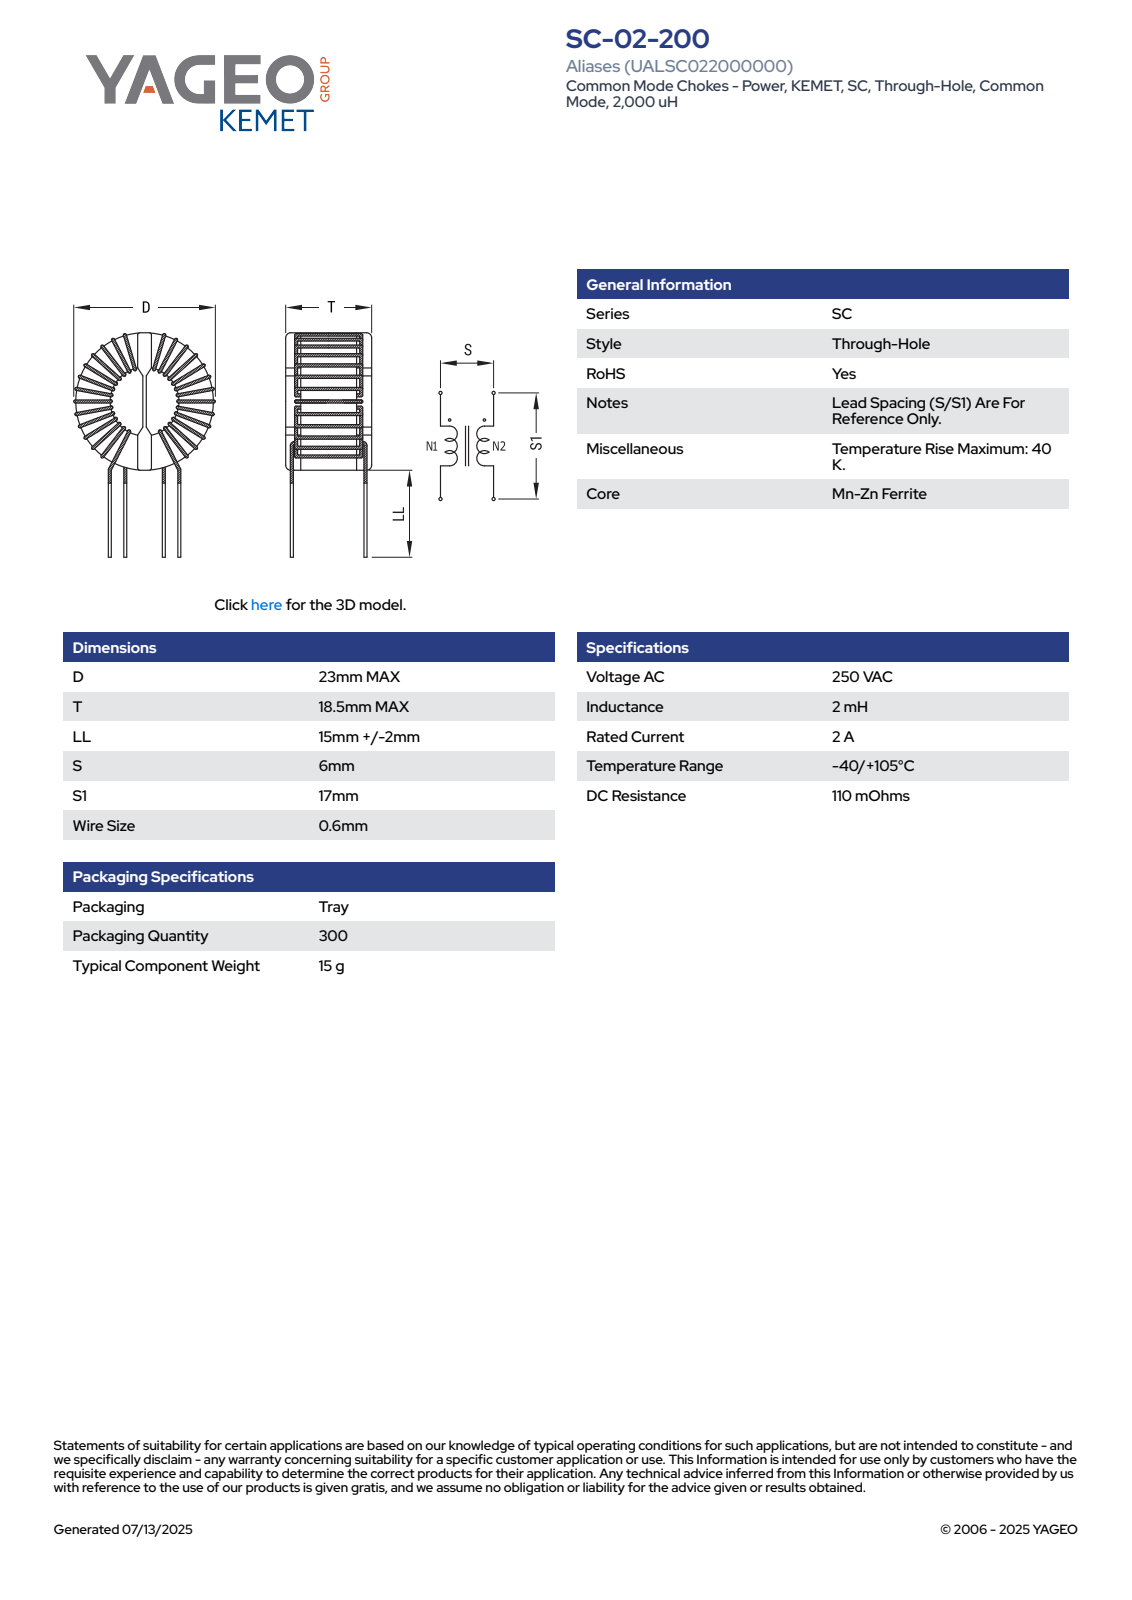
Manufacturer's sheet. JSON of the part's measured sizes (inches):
{"part_name": "SC-02-200", "step_written_by": "SolidWorks 2018 (AUTOMOTIVE_DESIGN)", "units": "inches", "bodies": {"solids": 1, "faces": 209, "planar": 62, "cylindrical": 79, "other": 68}, "overall_size": [1.432, 0.906, 0.728], "volume_in3": 0.361, "surface_area_in2": 5.456, "round_bosses_or_shafts": [[0.024, 8]], "partial_cylinders_radius": [[0.012, 16], [0.008, 4], [0.112, 1], [0.163, 1], [0.183, 1], [0.187, 1], [0.193, 1], [0.364, 1]], "face_to_face_distances": [0.642, 0.047, 0.079, 0.031, 0.043, 0.126, 0.685, 0.137, 0.505, 0.154]}
